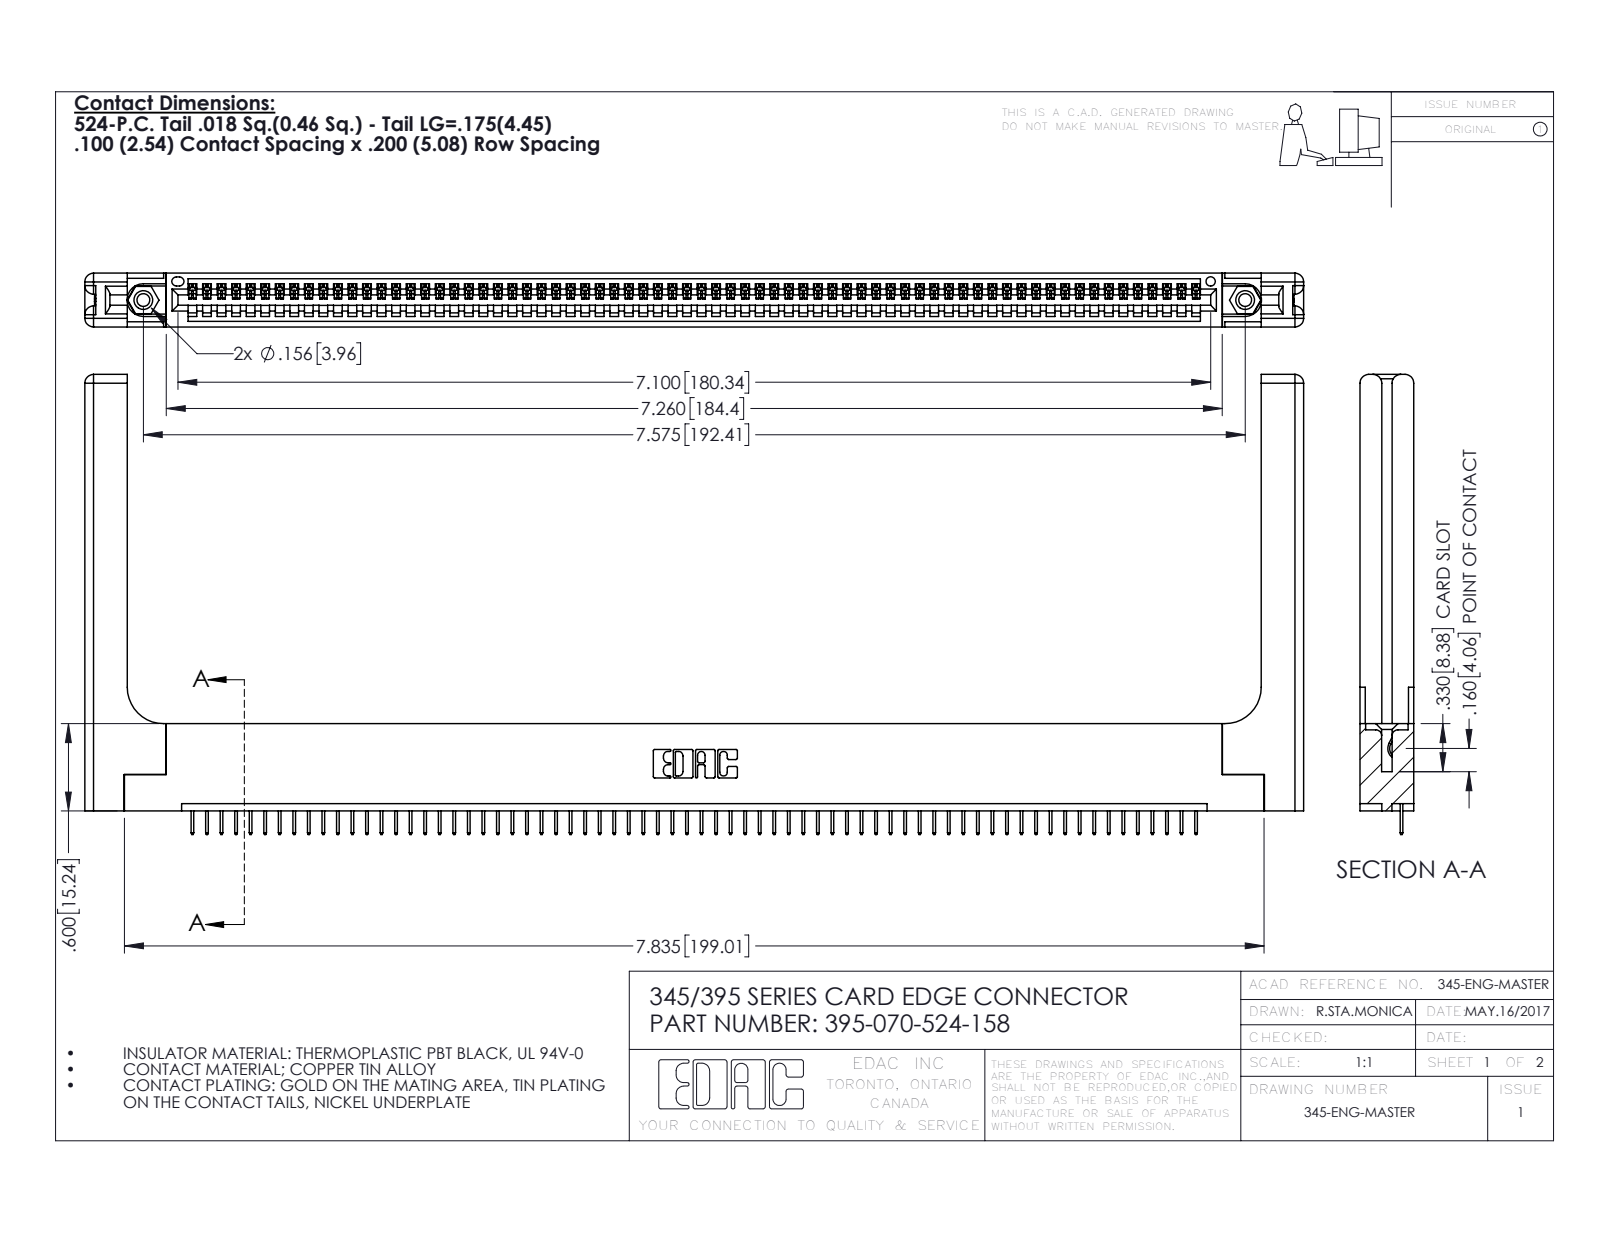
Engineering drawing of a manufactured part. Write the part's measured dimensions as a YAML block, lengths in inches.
part_name: "345 Part_Flush Mounting Lugs - 0.156 Dia-TH; 345-292-001_345-293-124; 345-250-001_345-250-001-102; 395-070-524-158 (+1 more)"
step_written_by: "SolidWorks 2016 (CONFIG_CONTROL_DESIGN)"
units: inches
bodies: {solids: 75, faces: 4722, planar: 3448, cylindrical: 1214, other: 60}
overall_size: [8.379, 3.162, 0.37]
volume: 1.75
surface_area: 48.98
round_holes:
  - {diameter: 0.089, count: 2}
  - {diameter: 0.125, count: 2}
  - {diameter: 0.156, count: 2}
  - {diameter: 0.064, count: 1}
round_bosses_or_shafts:
  - {diameter: 0.155, count: 2}
partial_cylinders:
  - {radius: 0.006, count: 140}
  - {radius: 0.01, count: 22}
  - {radius: 0.06, count: 16}
  - {radius: 0.007, count: 6}
  - {radius: 0.031, count: 6}
  - {radius: 0.026, count: 3}
  - {radius: 0.03, count: 2}
  - {radius: 0.031, count: 2}
face_to_face_distances: [0.072, 0.37, 0.298, 0.2, 0.098, 0.272, 0.025, 0.225, 0.148, 0.15]
hole_center_spacings: [0.27, 7.339, 7.575]
